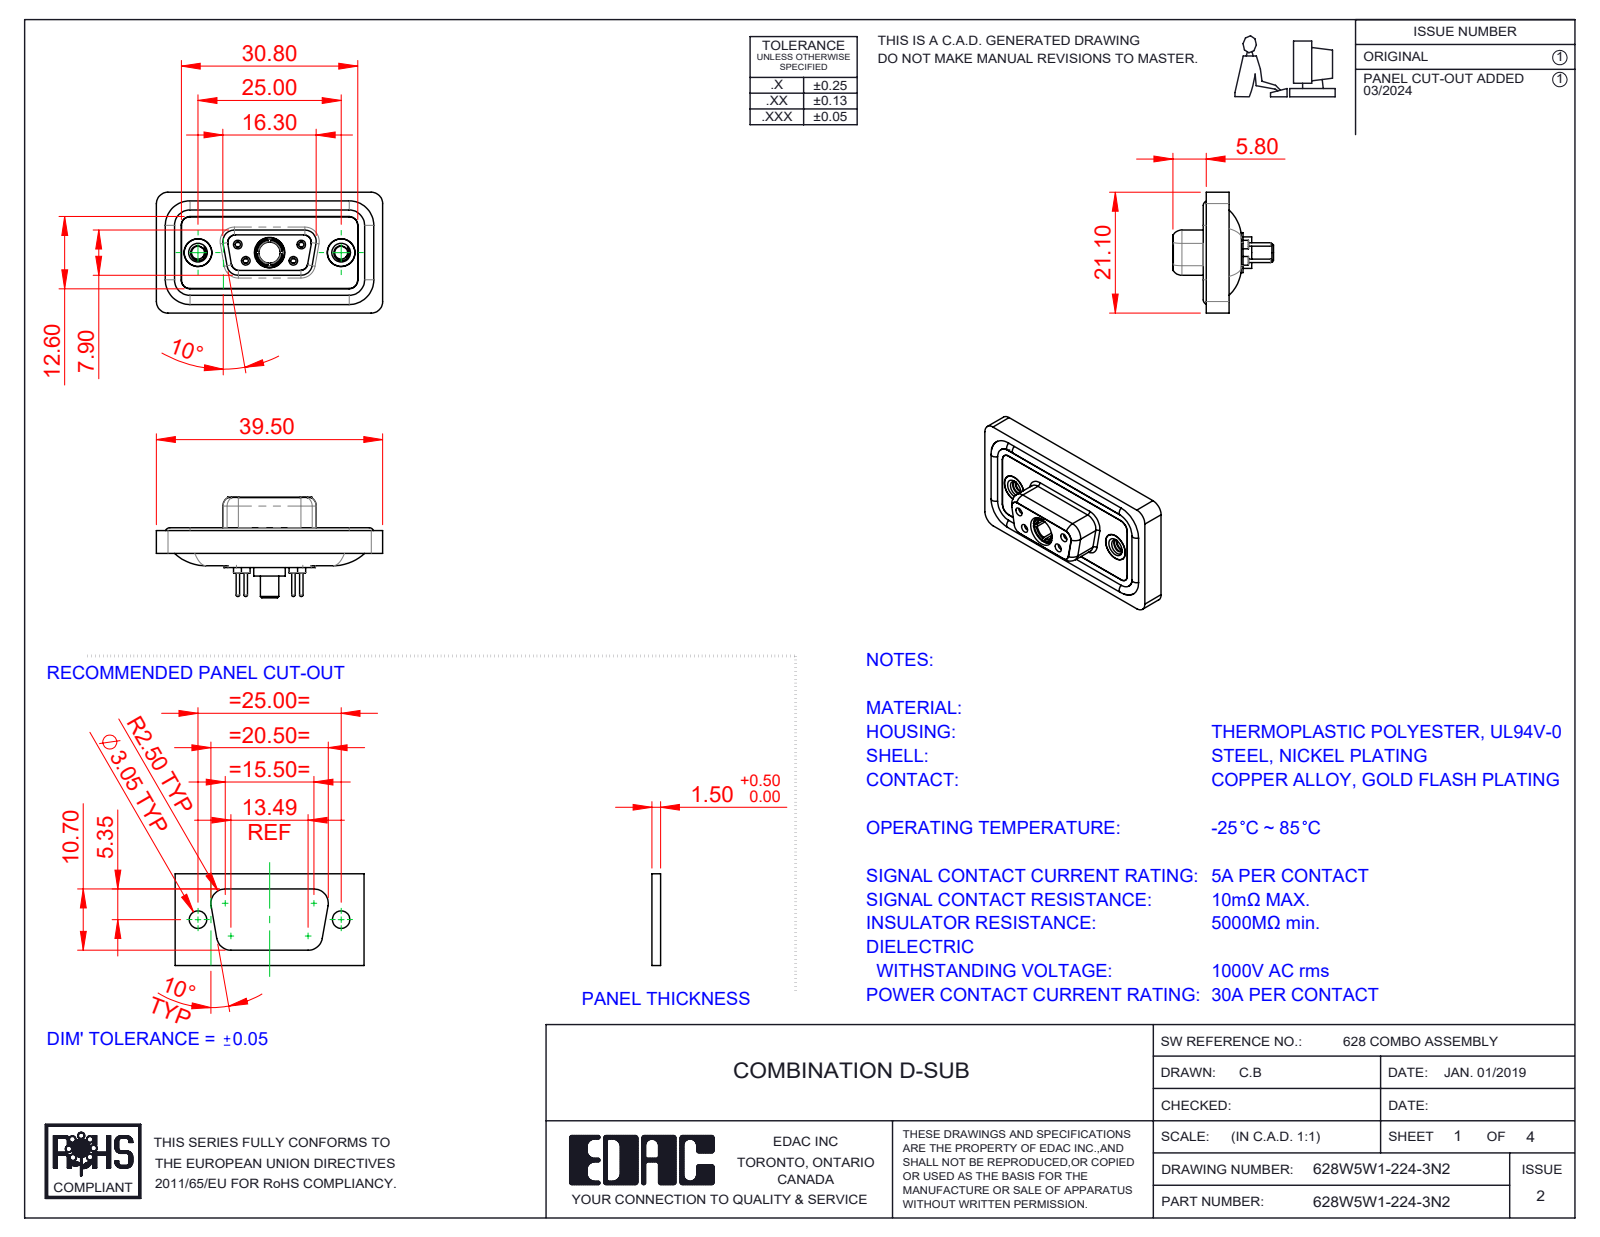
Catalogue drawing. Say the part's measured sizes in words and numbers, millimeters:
The part is named "628Combo Contact Row 1_24; 628Combo Contact Row 2_24; 628Combo Shell Rear_09 Contacts; 628Combo Waterproof Housing_09 Contacts (+5 more)". Its 3-D file was written by "SolidWorks 2023 (CONFIG_CONTROL_DESIGN)". It is 13 solids with 680 faces: 194 planar, 287 cylindrical and 199 other. Overall it measures 39.5 by 21.1 by 17.55 millimeters. Its volume is 4 774 cubic millimeters and its surface area 7 640 square millimeters. Round holes: 4 of diameter 0.9, 4 of diameter 1.1, 4 of diameter 1.5, 4 of diameter 2, 3 of diameter 4.85, 2 of diameter 1.6, 2 of diameter 1.7, 2 of diameter 2.26, 2 of diameter 4, 2 of diameter 4.05, 2 of diameter 5, 1 of diameter 3.7. Round bosses or shafts: 6 of diameter 1.6, 4 of diameter 2.2, 4 of diameter 0.6, 2 of diameter 4.95, 2 of diameter 4.8, 1 of diameter 5.5, 1 of diameter 5.2, 1 of diameter 4.96. Partial cylindrical surfaces (rounded edges, fillets, slot ends): 22 of radius 1.5, 18 of radius 2, 8 of radius 1.35, 8 of radius 1.6, 4 of radius 0.25, 4 of radius 0.5, 4 of radius 0.6, 4 of radius 0.65. The main face-to-face distances are 0.4, 2.9, 1.1, 1.8, 1.6, 0.5, 5.65, 7.45, 5.35, 3.6. The hole center spacings are 3.16, 5.72, 7.1, 12.5, 18.1, 4.39, 4.4, 8.31.
